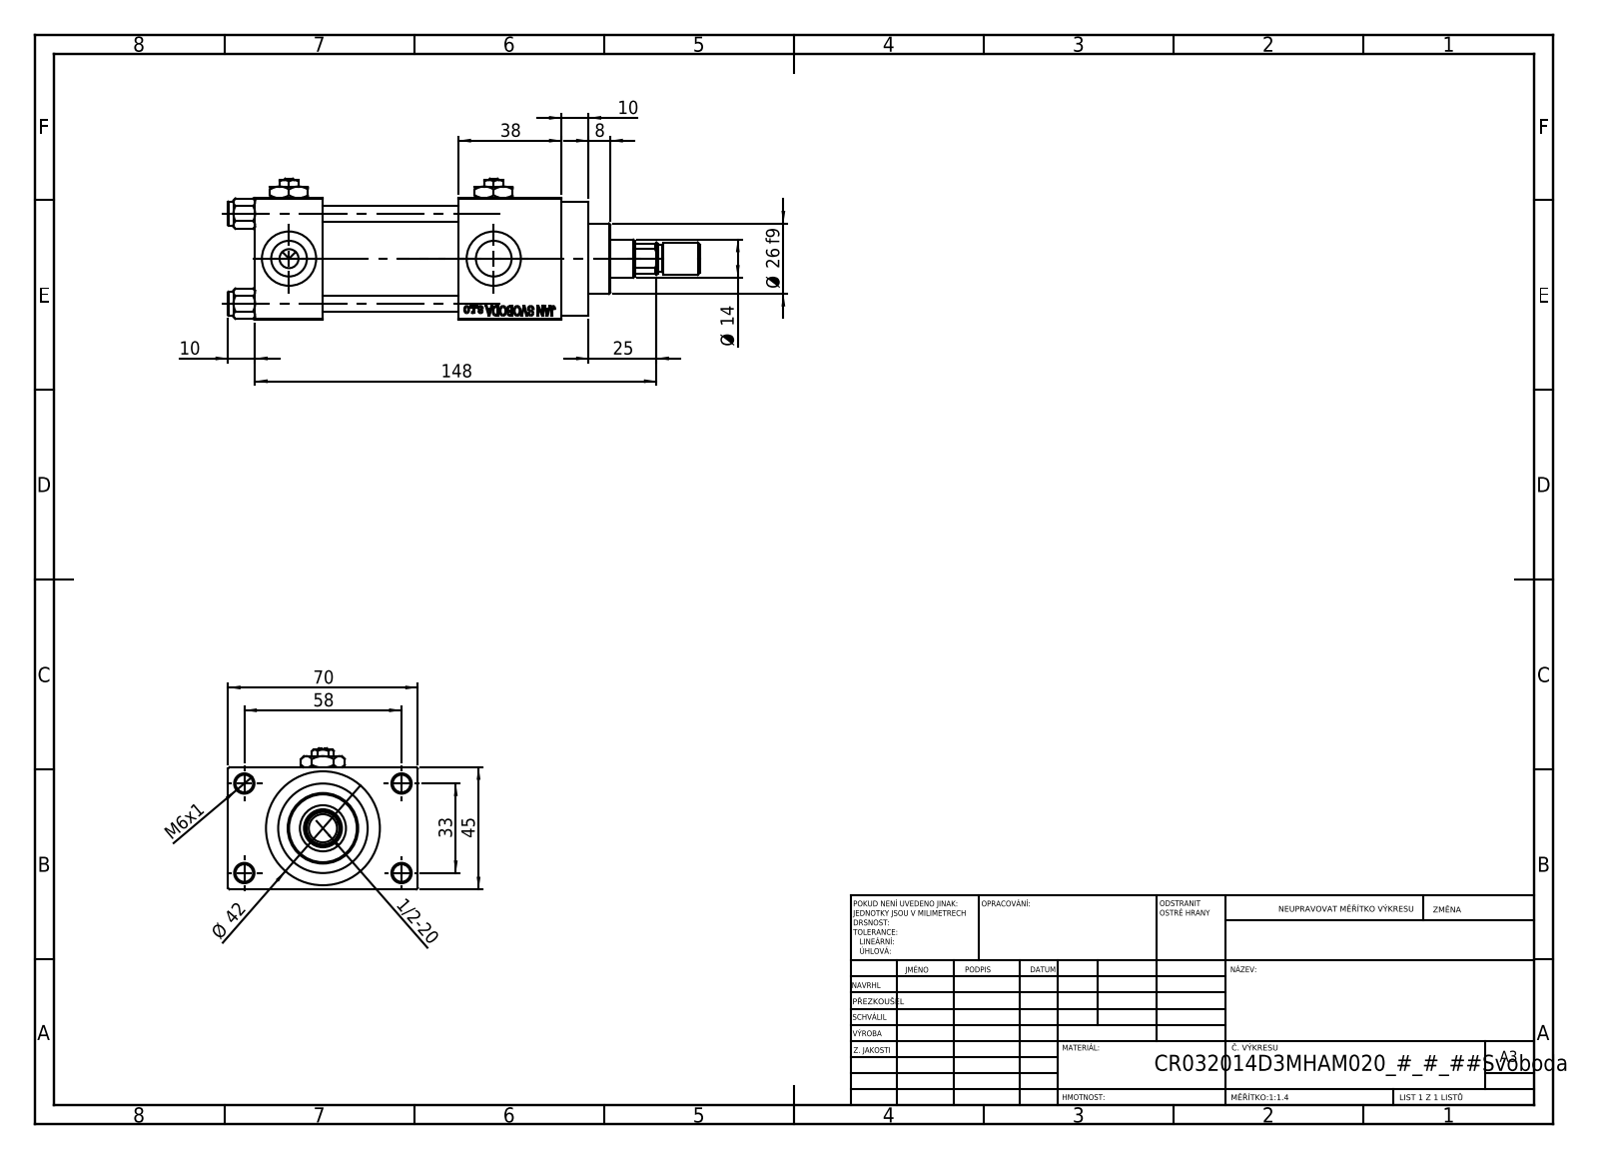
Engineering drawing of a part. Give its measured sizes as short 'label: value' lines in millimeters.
name: ROD_END_AH; NUT_M5_D; V215CR_D_Body; Zatka_pro_OIL_PORT (+3 more)
written by: SolidWorks 2019 (CONFIG_CONTROL_DESIGN)
unit: mm
bodies: 14 solids, 1215 faces (546 planar, 103 cylindrical, 566 other)
size: 174 × 70 × 52
volume: 230 802 mm³; area: 77 978 mm²
holes: 5× ⌀6.5, 4× ⌀6, 4× ⌀13.16, 4× ⌀20, 3× ⌀7, 1× ⌀14, 1× ⌀17, 1× ⌀24, 1× ⌀32, 1× ⌀33
bosses: 4× ⌀9, 1× ⌀42, 1× ⌀38, 1× ⌀26, 1× ⌀12, 1× ⌀10
rounds: 1× R6.5
face distances: 45, 25, 50, 12.5, 75, 57.5, 88, 38, 113, 70
hole spacings: 12.4, 23.48, 33.2, 33.37, 35.35, 45.6, 56.35, 33
